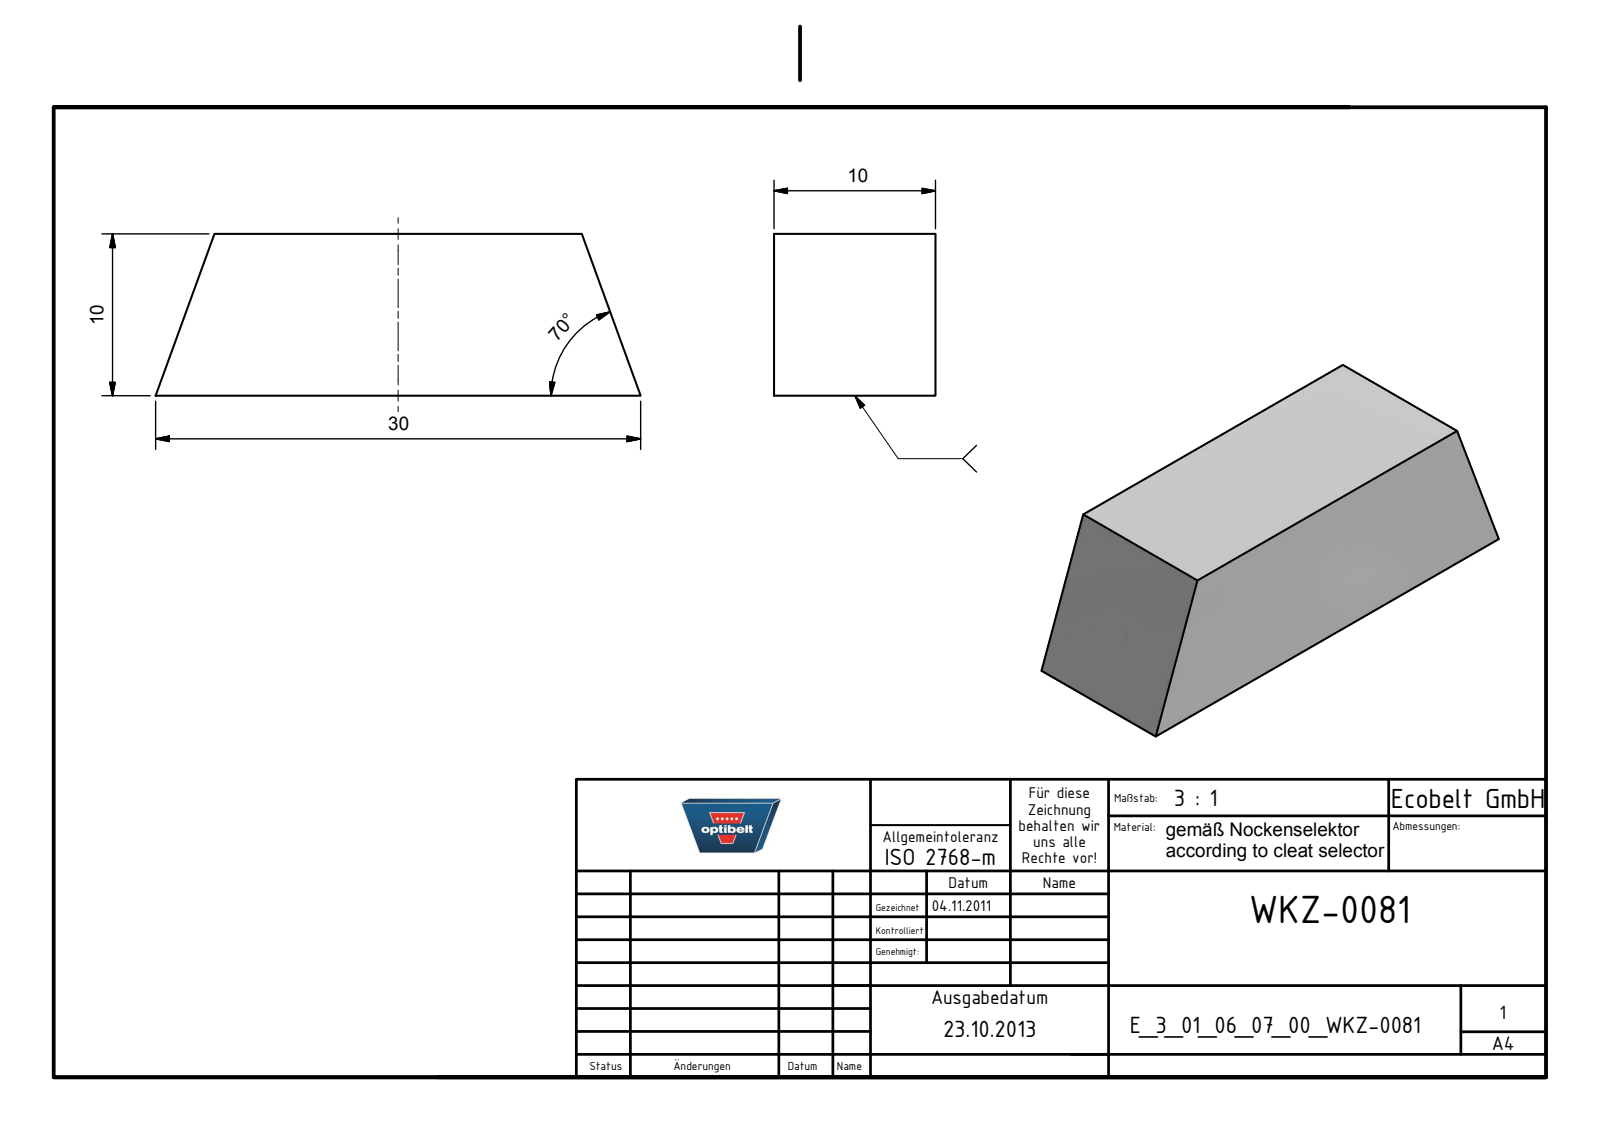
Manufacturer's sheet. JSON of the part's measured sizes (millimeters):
{"part_name": "E_3_01_06_07_00_WKZ-0081", "step_written_by": "Autodesk Inventor 2025 (AUTOMOTIVE_DESIGN)", "units": "millimeters", "bodies": {"solids": 1, "faces": 6, "planar": 6, "cylindrical": 0, "other": 0}, "overall_size": [30, 10, 10], "volume_mm3": 2636, "surface_area_mm2": 1267, "face_to_face_distances": [10]}
